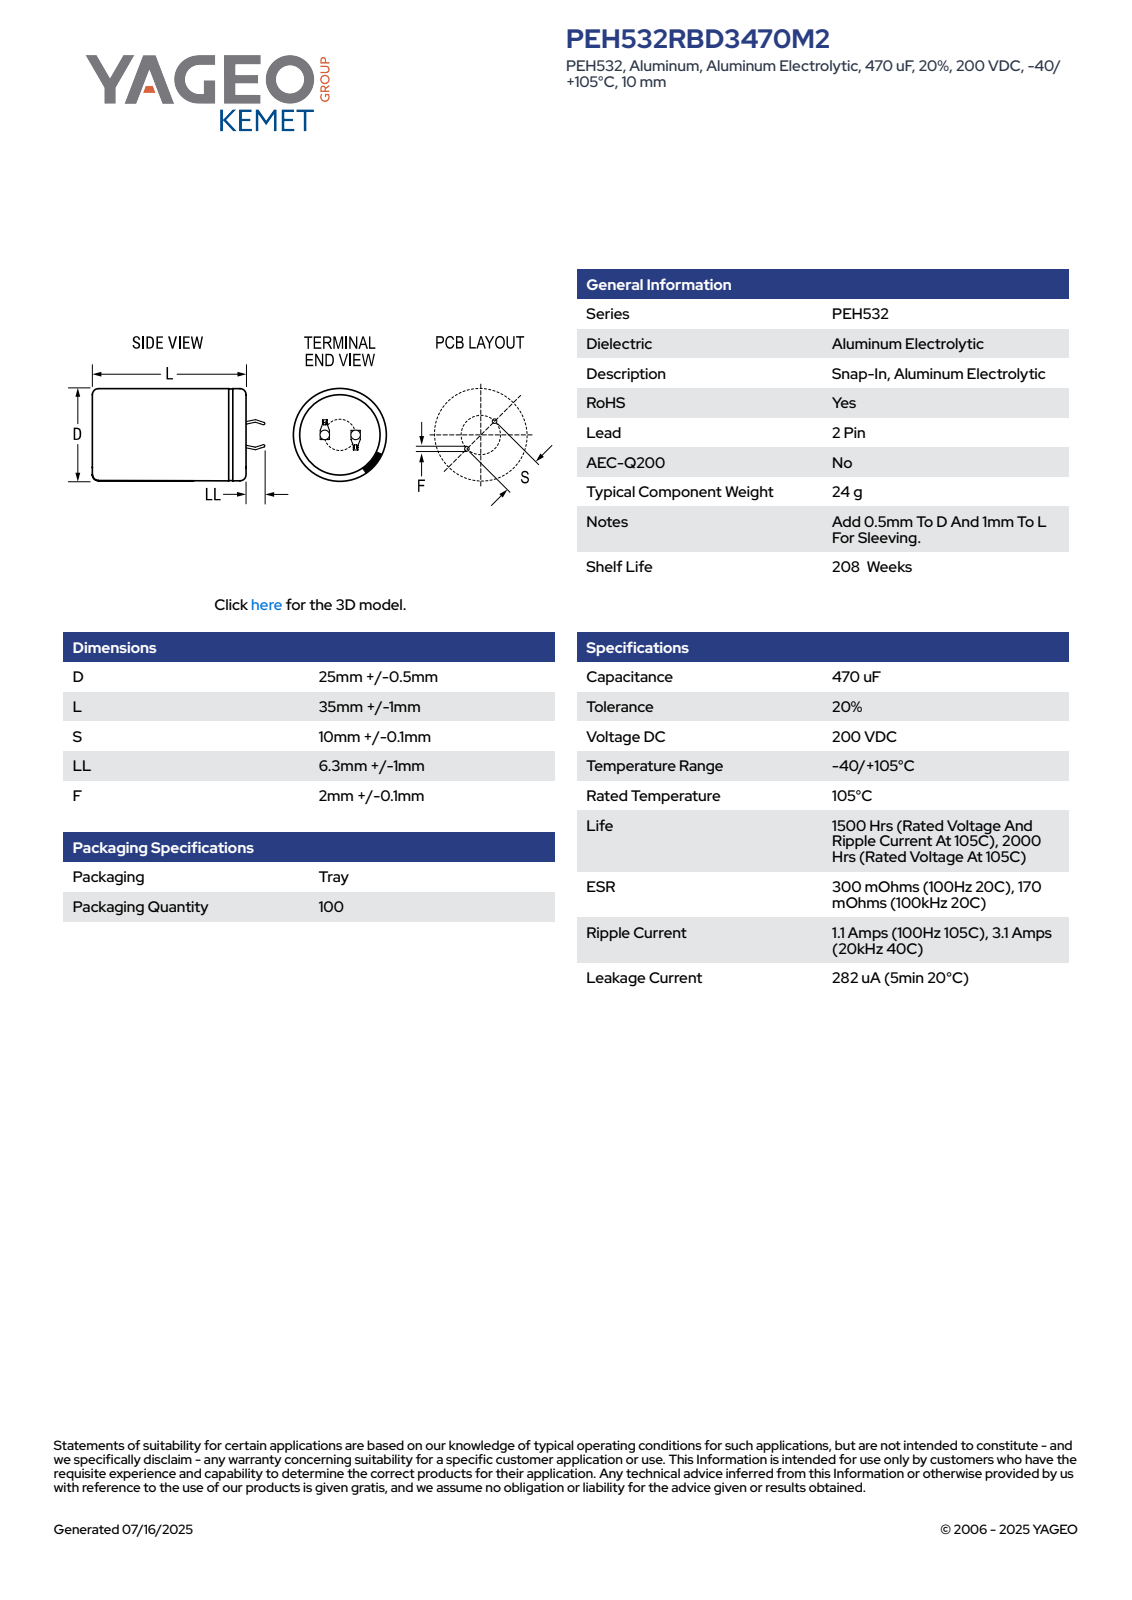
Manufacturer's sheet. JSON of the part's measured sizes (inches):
{"part_name": "CARS_K2P_25X35_D25.5L36S10LL7.3F2.1", "step_written_by": "SolidWorks 2014 (AUTOMOTIVE_DESIGN)", "units": "inches", "bodies": {"solids": 1, "faces": 100, "planar": 52, "cylindrical": 9, "other": 39}, "overall_size": [1.704, 1.004, 1.004], "volume_in3": 1.111, "surface_area_in2": 6.088, "round_holes": [[0.888, 1]], "round_bosses_or_shafts": [[1.004, 1]], "partial_cylinders_radius": [[0.502, 1]], "face_to_face_distances": [1.417, 0.024, 1.437, 0.02, 0.279, 0.301, 0.03, 0.053, 0.302, 0.255]}
